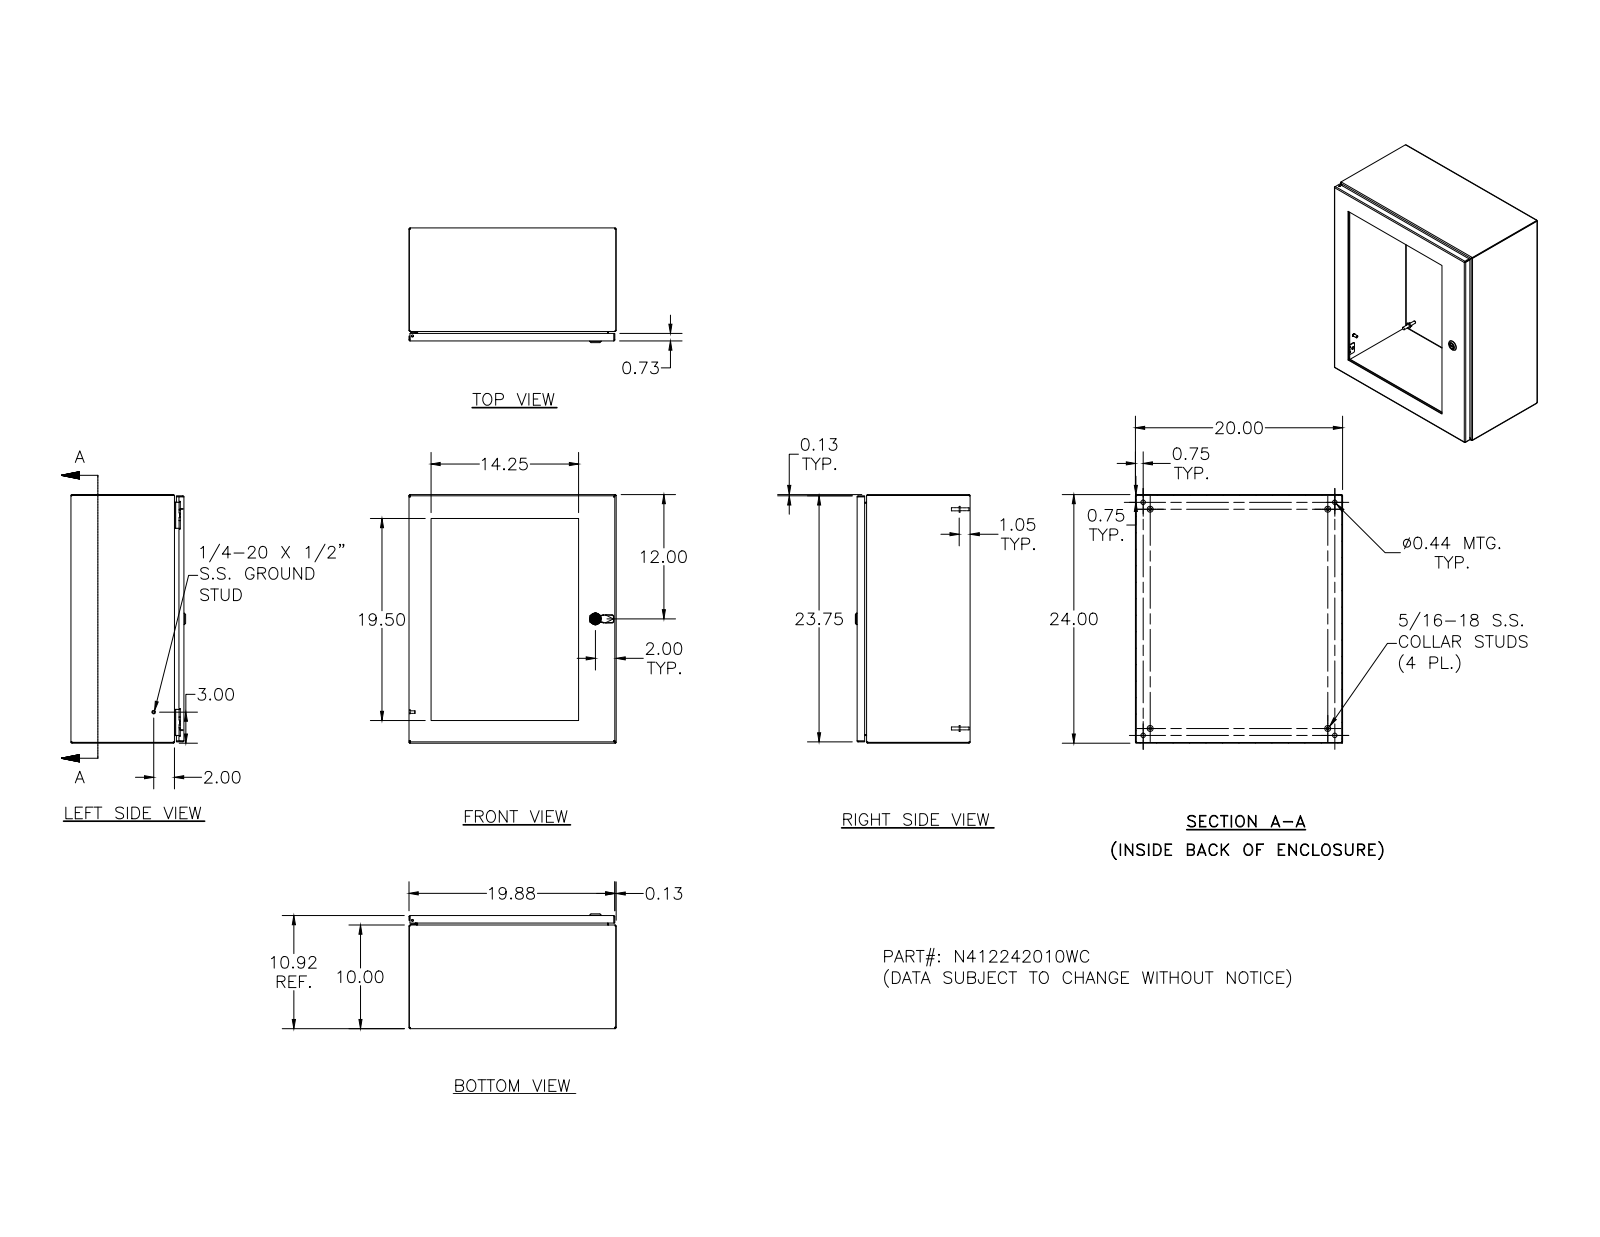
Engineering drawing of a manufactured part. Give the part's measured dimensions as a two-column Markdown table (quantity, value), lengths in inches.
| quantity | value |
| --- | --- |
| part name | N412242010WC |
| STEP written by | SolidWorks 2018 (AUTOMOTIVE_DESIGN) |
| units | inches |
| bodies | 73 solids, 2083 faces (775 planar, 625 cylindrical, 683 other) |
| overall size | 24 × 20 × 11.075 |
| volume | 212.8 in³ |
| surface area | 4 324 in² |
| round holes (diameter × count) | 0.156 × 20, 0.281 × 18, 0.188 × 5, 0.093 × 4, 0.152 × 4, 0.167 × 4, 0.172 × 4, 0.437 × 4, 0.187 × 1, 0.197 × 1, 0.315 × 1, 0.394 × 1 |
| round bosses / shafts (diameter × count) | 0.337 × 18, 0.19 × 18, 0.25 × 10, 0.563 × 4, 0.36 × 4, 0.32 × 4, 0.3 × 4, 0.275 × 4 |
| partial cylindrical surfaces (radius × count) | 0.031 × 34, 0.012 × 30, 0.05 × 26, 0.105 × 24, 0.016 × 18, 0.125 × 16, 0.02 × 13, 0.032 × 8 |
| main face-to-face distances | 0.074, 10.843, 10.769, 19.926, 23.926, 0.25, 10.593, 10.519, 20, 19.852 |
| hole center spacings | 4, 8, 16.008, 12, 17.443, 20, 21.132, 15.5 |
